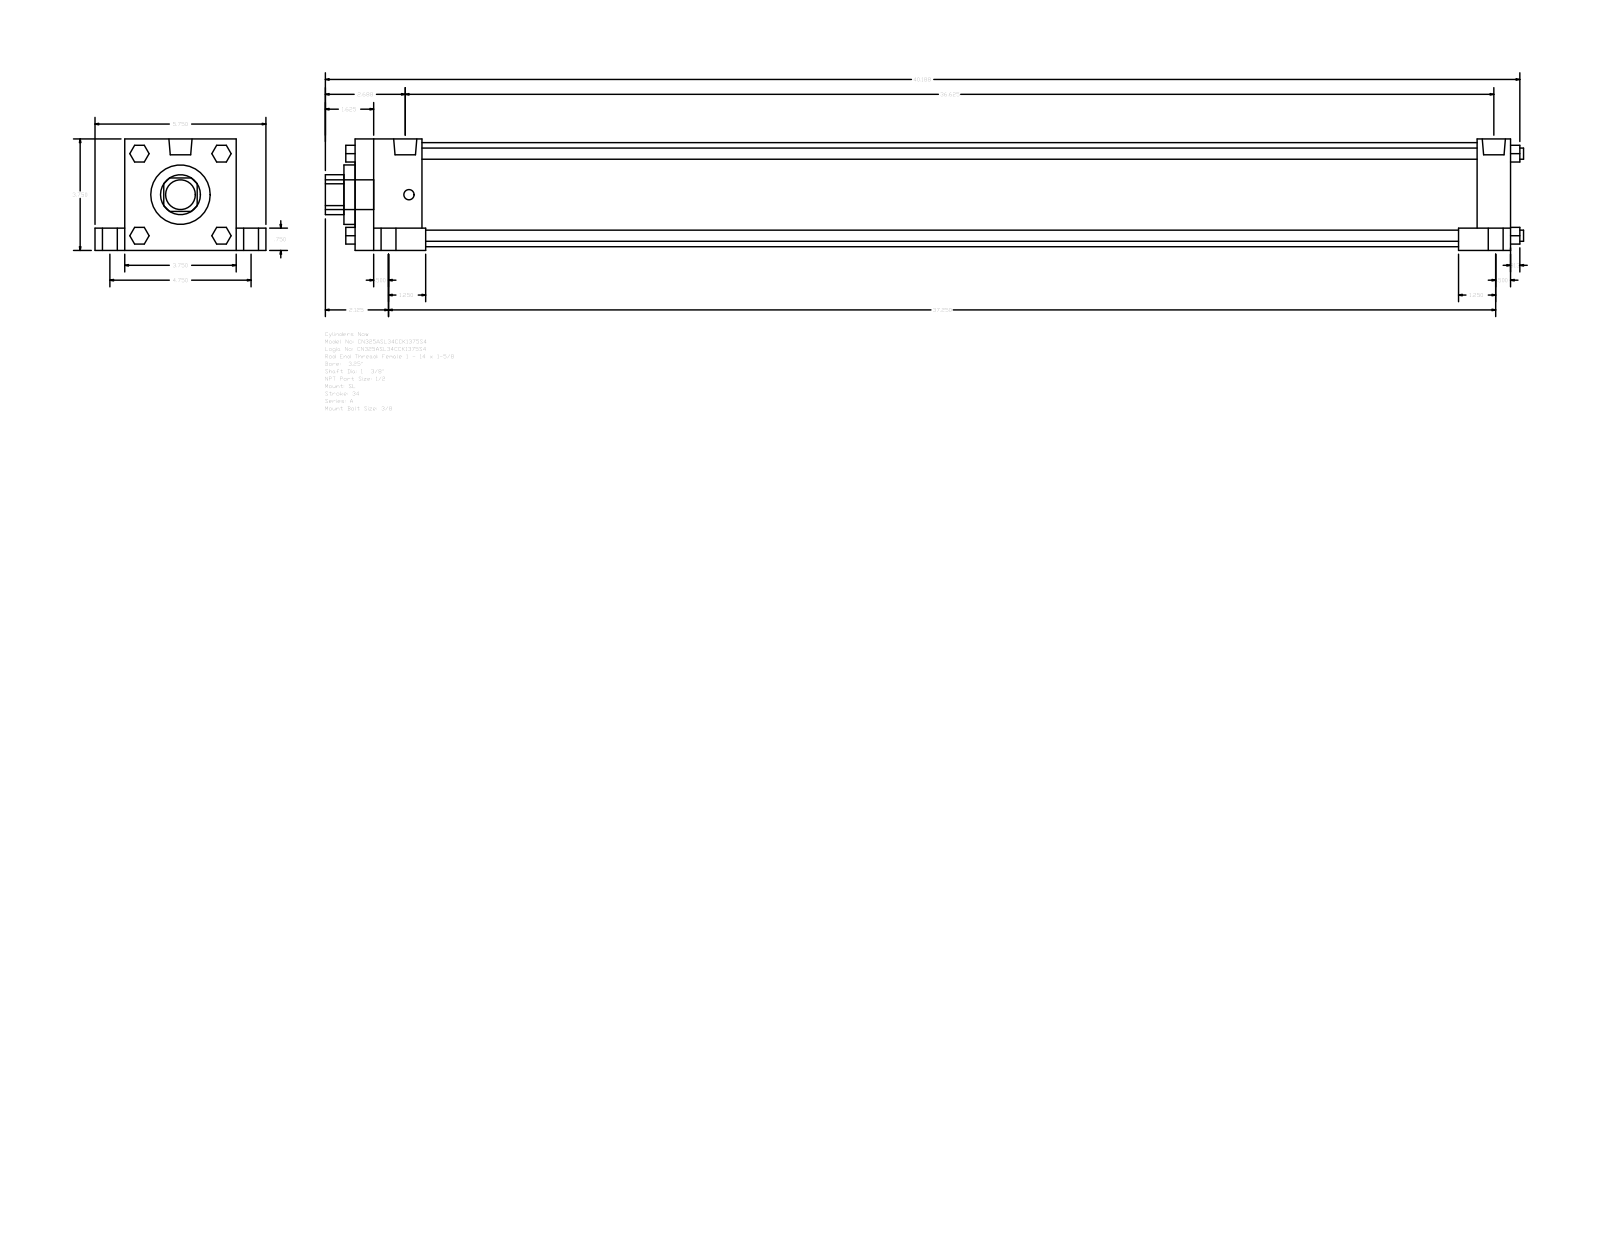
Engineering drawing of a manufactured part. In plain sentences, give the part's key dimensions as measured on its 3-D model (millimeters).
The part is named "A_SL__0325_1.375". Its 3-D file was written by "GSSL Pune (CONFIG_CONTROL_DESIGN)". It is 0 solids with 150 faces: 114 planar, 36 cylindrical and 0 other. Overall it measures 1023.94 by 146.05 by 95.25 millimeters. Round holes: 1 of diameter 34.92, 1 of diameter 50.8, 1 of diameter 88.9. Round bosses or shafts: 4 of diameter 19.05, 4 of diameter 12.7, 4 of diameter 9.53, 4 of diameter 8.73, 2 of diameter 19.77, 1 of diameter 25.4. Partial cylindrical surfaces (rounded edges, fillets, slot ends): 1 of radius 17.06. The main face-to-face distances are 95.24, 987.43, 25.41, 120.65, 19.05, 76.19, 15.87, 28.58, 57.15, 958.85.
